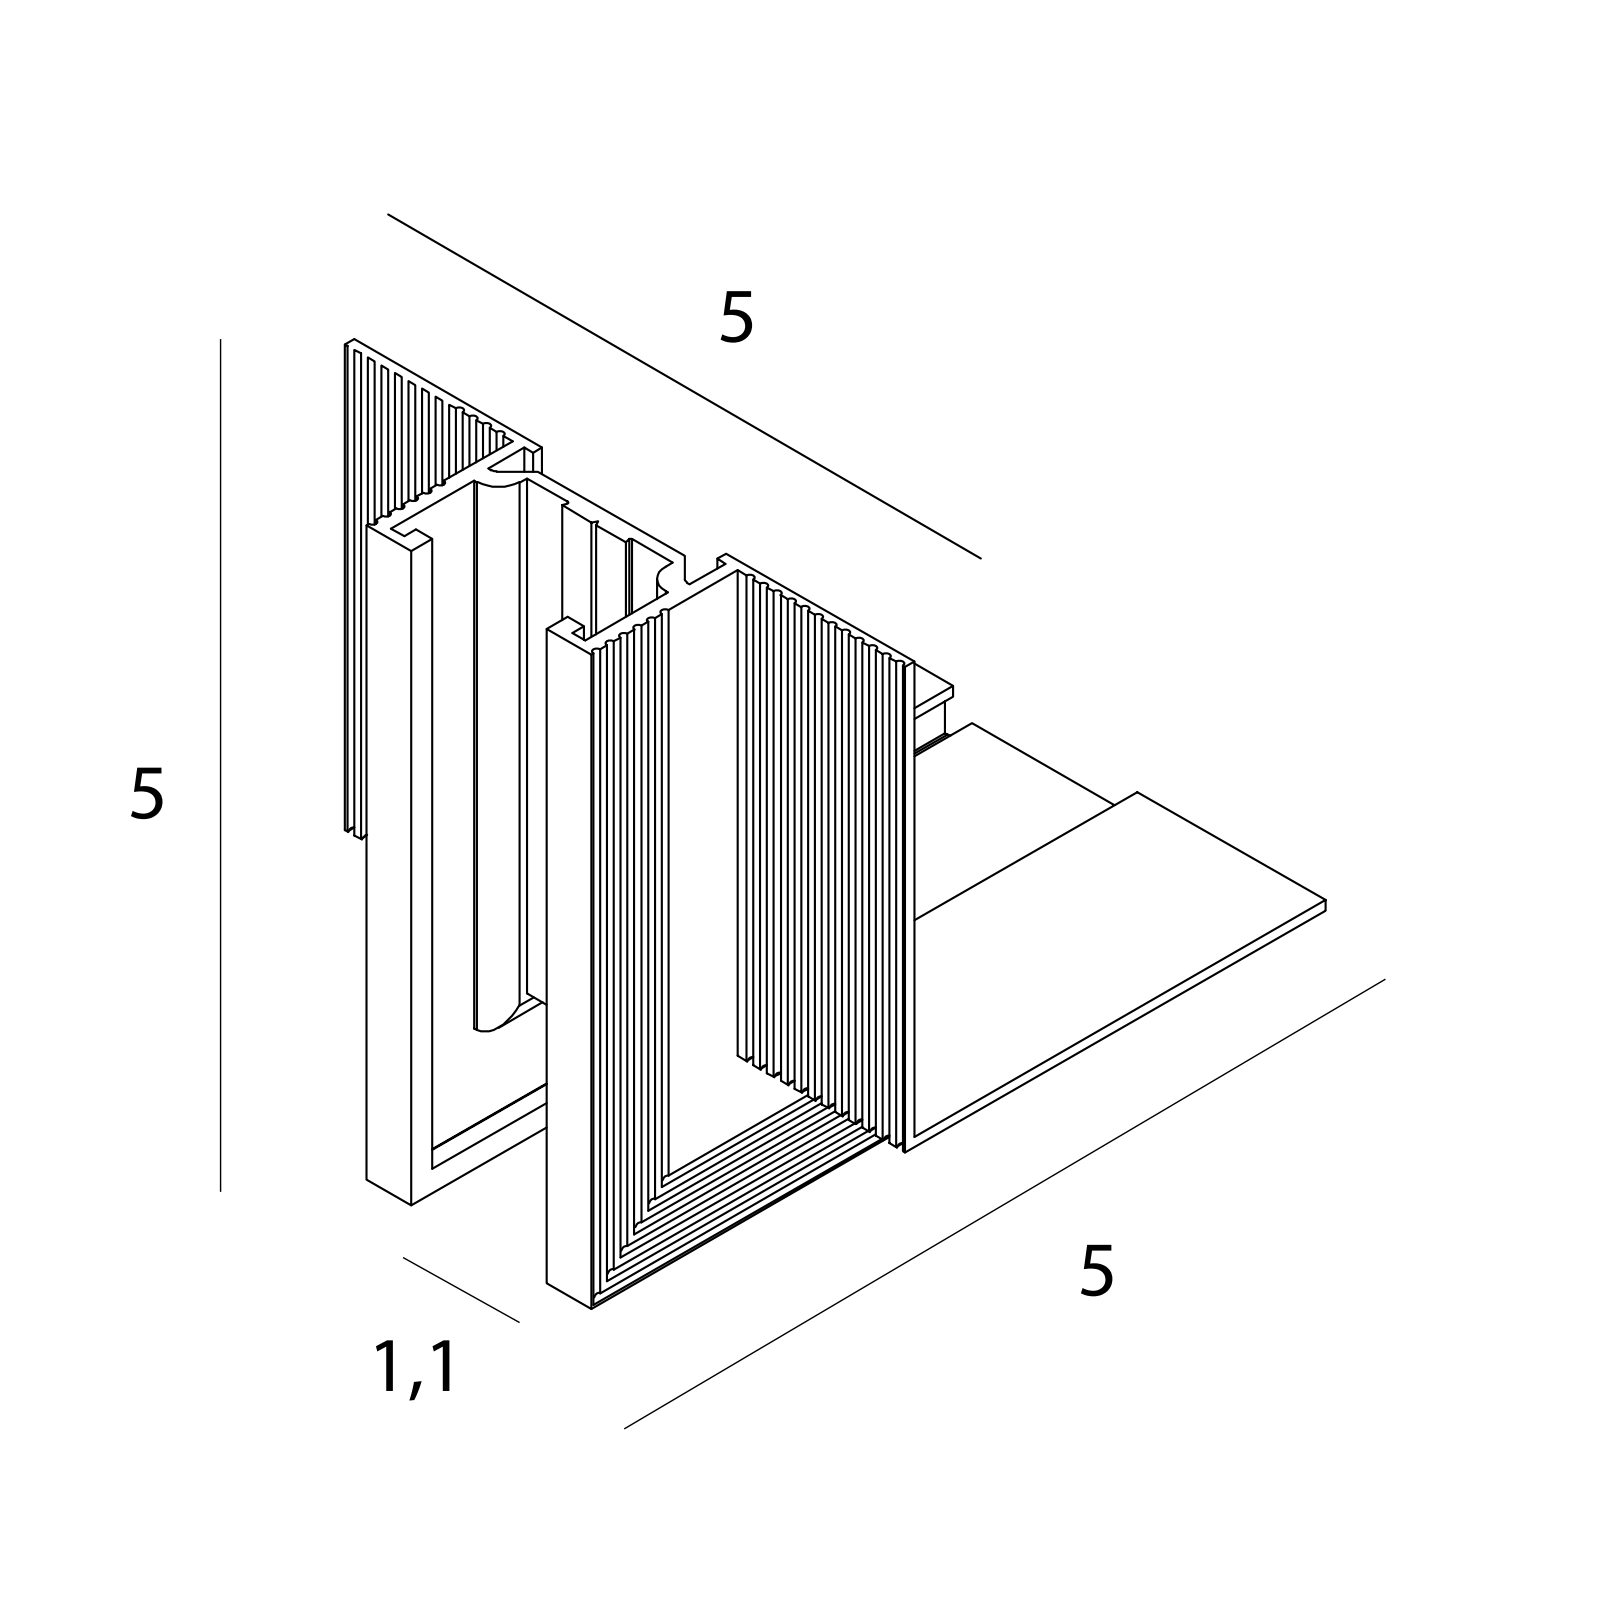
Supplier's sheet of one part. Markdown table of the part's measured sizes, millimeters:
| quantity | value |
| --- | --- |
| part name | NT0005 v2 |
| STEP written by | Autodesk Translation Framework v14.24.0.0 (AUTOMOTIVE_DESIGN) |
| units | millimeters |
| bodies | 1 solid, 216 faces (132 planar, 84 cylindrical, 0 other) |
| overall size | 50 × 50 × 49.47 |
| volume | 7 083 mm³ |
| surface area | 15 322 mm² |
| partial cylindrical surfaces (radius × count) | 0.3 × 72, 0.1 × 4, 0.5 × 4, 1.9 × 4 |
| main face-to-face distances | 0.8, 1.35, 18.47, 12.9, 2.04, 1.24, 13.7, 11.66, 19.82, 17.12 |
